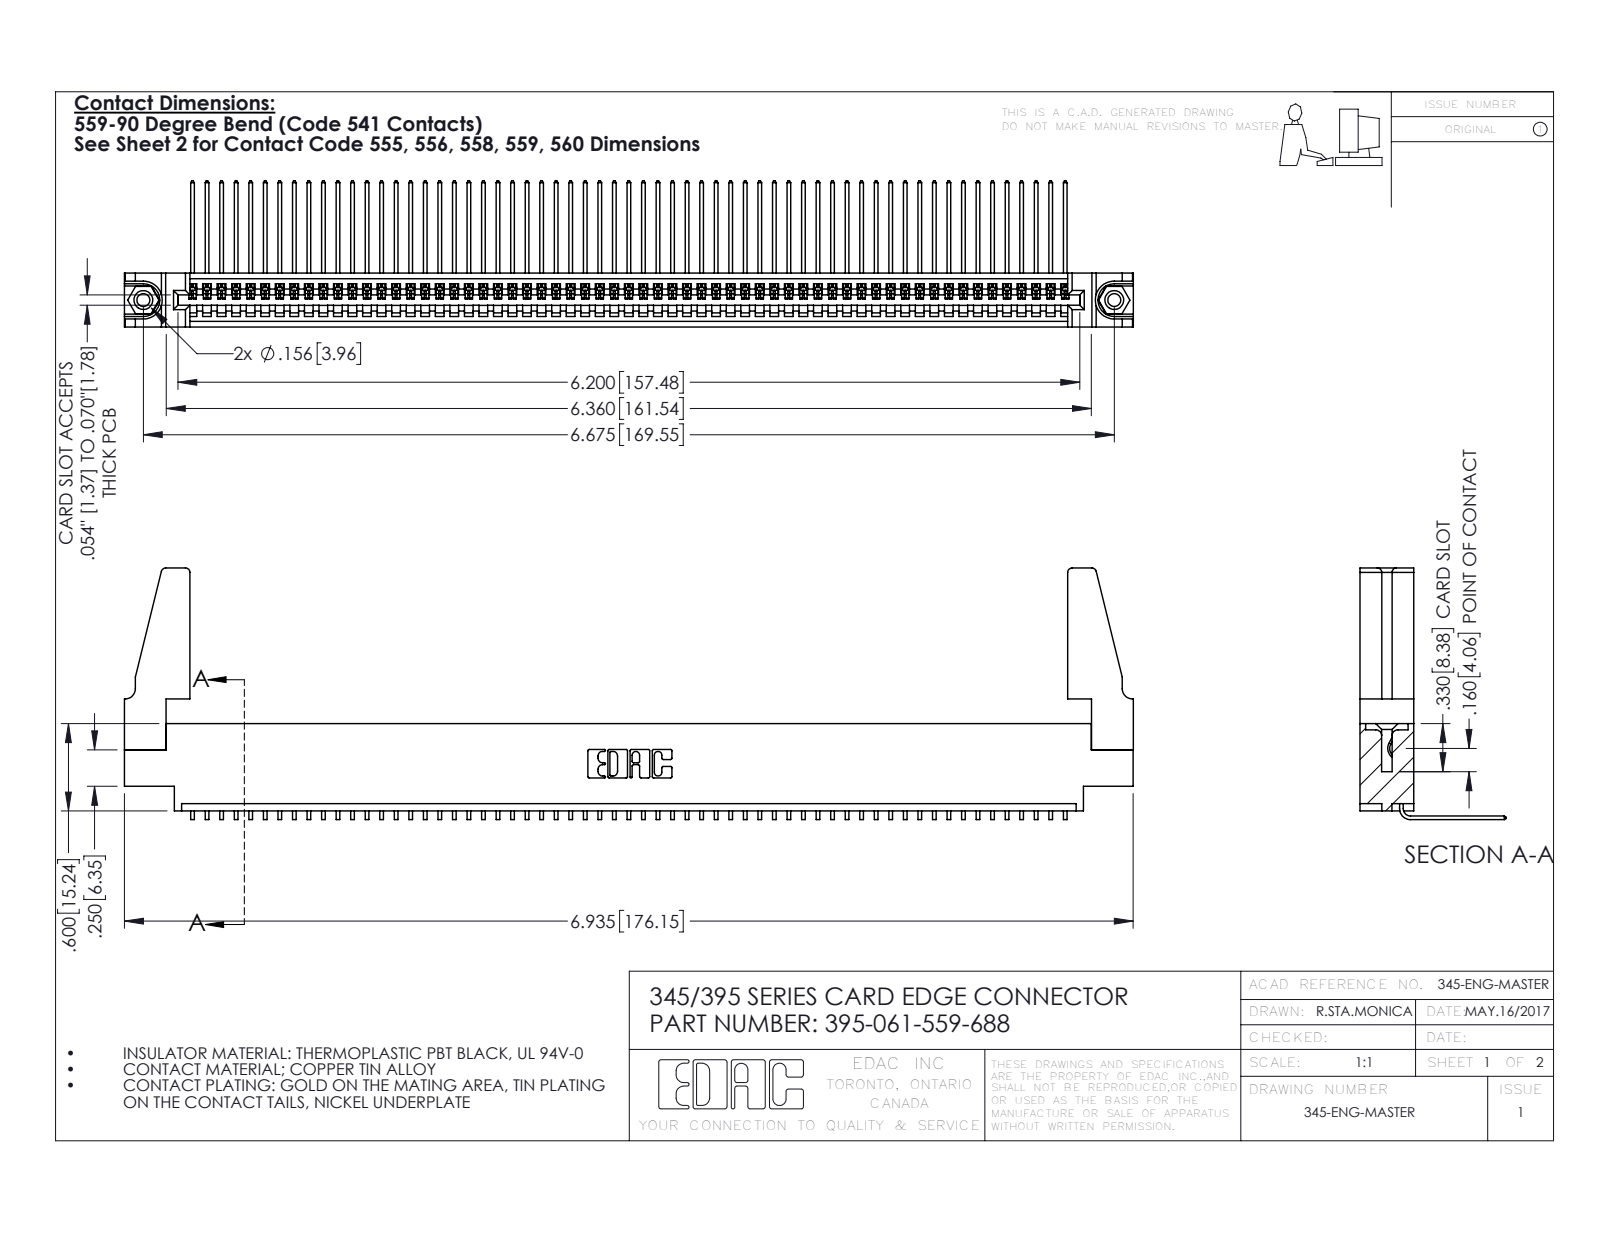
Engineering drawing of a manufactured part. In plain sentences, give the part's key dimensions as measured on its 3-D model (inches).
The part is named "345-250-001_345-250-001-102; 345 Part_0.170 Offset - 0.156 Dia-TH; 395-061-559-688; 345-220-078_345-220-088 (+1 more)". Its 3-D file was written by "SolidWorks 2016 (CONFIG_CONTROL_DESIGN)". It is 66 solids with 3914 faces: 2718 planar, 1180 cylindrical and 16 other. Overall it measures 6.936 by 1.729 by 1.005 inches. Its volume is 1.235 cubic inches and its surface area 42.27 square inches. Round holes: 2 of diameter 0.089, 2 of diameter 0.125, 2 of diameter 0.156, 1 of diameter 0.064. Round bosses or shafts: 2 of diameter 0.155. Partial cylindrical surfaces (rounded edges, fillets, slot ends): 122 of radius 0.006, 22 of radius 0.01, 8 of radius 0.03, 6 of radius 0.007, 6 of radius 0.031, 3 of radius 0.026, 2 of radius 0.031, 2 of radius 0.04. The main face-to-face distances are 0.072, 0.298, 0.37, 0.098, 0.272, 0.025, 0.2, 0.225, 0.175, 0.149. The hole center spacings are 0.27, 6.439, 6.675.
